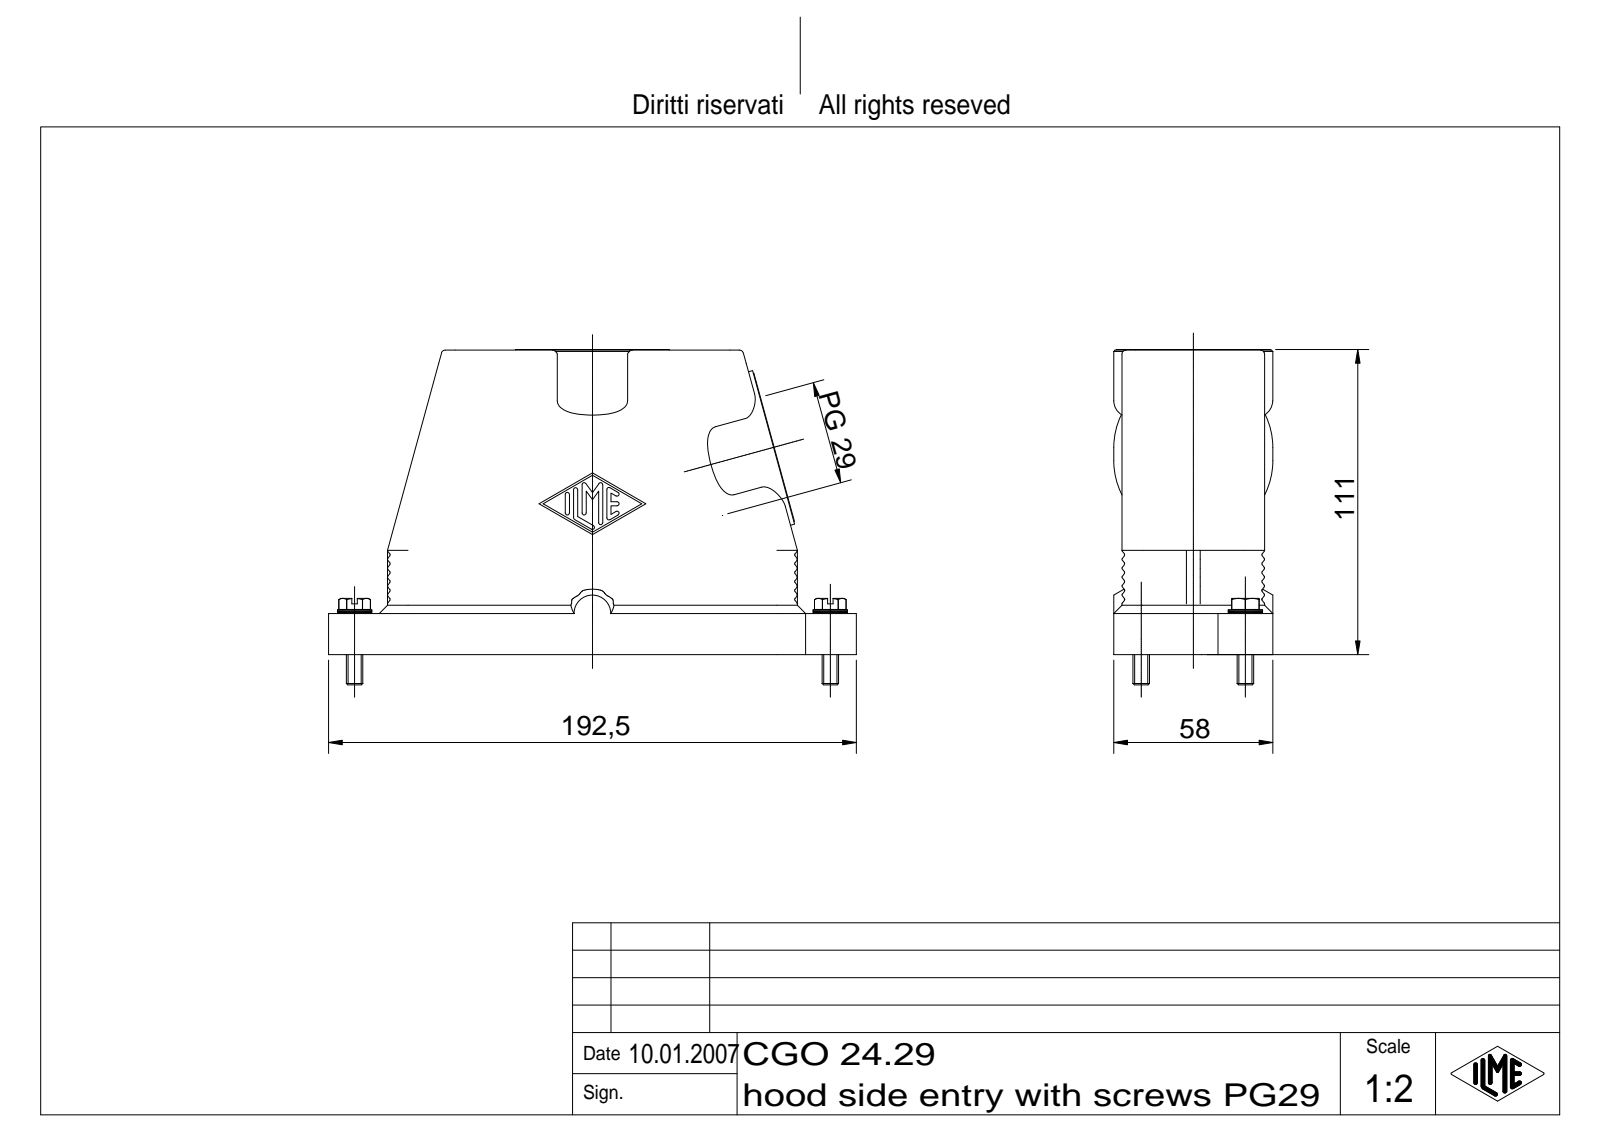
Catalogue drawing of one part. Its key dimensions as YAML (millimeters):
part_name: "CGO 24.29"
step_written_by: "Autodesk Inventor 7 (AUTOMOTIVE_DESIGN)"
units: millimeters
bodies: {solids: 3, faces: 767, planar: 189, cylindrical: 195, other: 383}
overall_size: [192.5, 122.2, 58]
volume: 251822
surface_area: 107397
round_holes:
  - {diameter: 2.46, count: 2}
  - {diameter: 3.2, count: 2}
  - {diameter: 6.6, count: 2}
  - {diameter: 15, count: 2}
  - {diameter: 35.48, count: 1}
round_bosses_or_shafts:
  - {diameter: 58, count: 2}
  - {diameter: 56, count: 2}
  - {diameter: 12.5, count: 2}
  - {diameter: 6, count: 2}
partial_cylinders:
  - {radius: 0.5, count: 39}
  - {radius: 0.75, count: 14}
  - {radius: 7.5, count: 8}
  - {radius: 6, count: 6}
  - {radius: 1.5, count: 4}
  - {radius: 3, count: 4}
  - {radius: 5.75, count: 2}
  - {radius: 10.5, count: 2}
face_to_face_distances: [3, 52, 49, 46, 6, 55, 2.5, 0.5, 58, 3.5]
hole_center_spacings: [35.18, 142.51, 107.45, 177.61]
